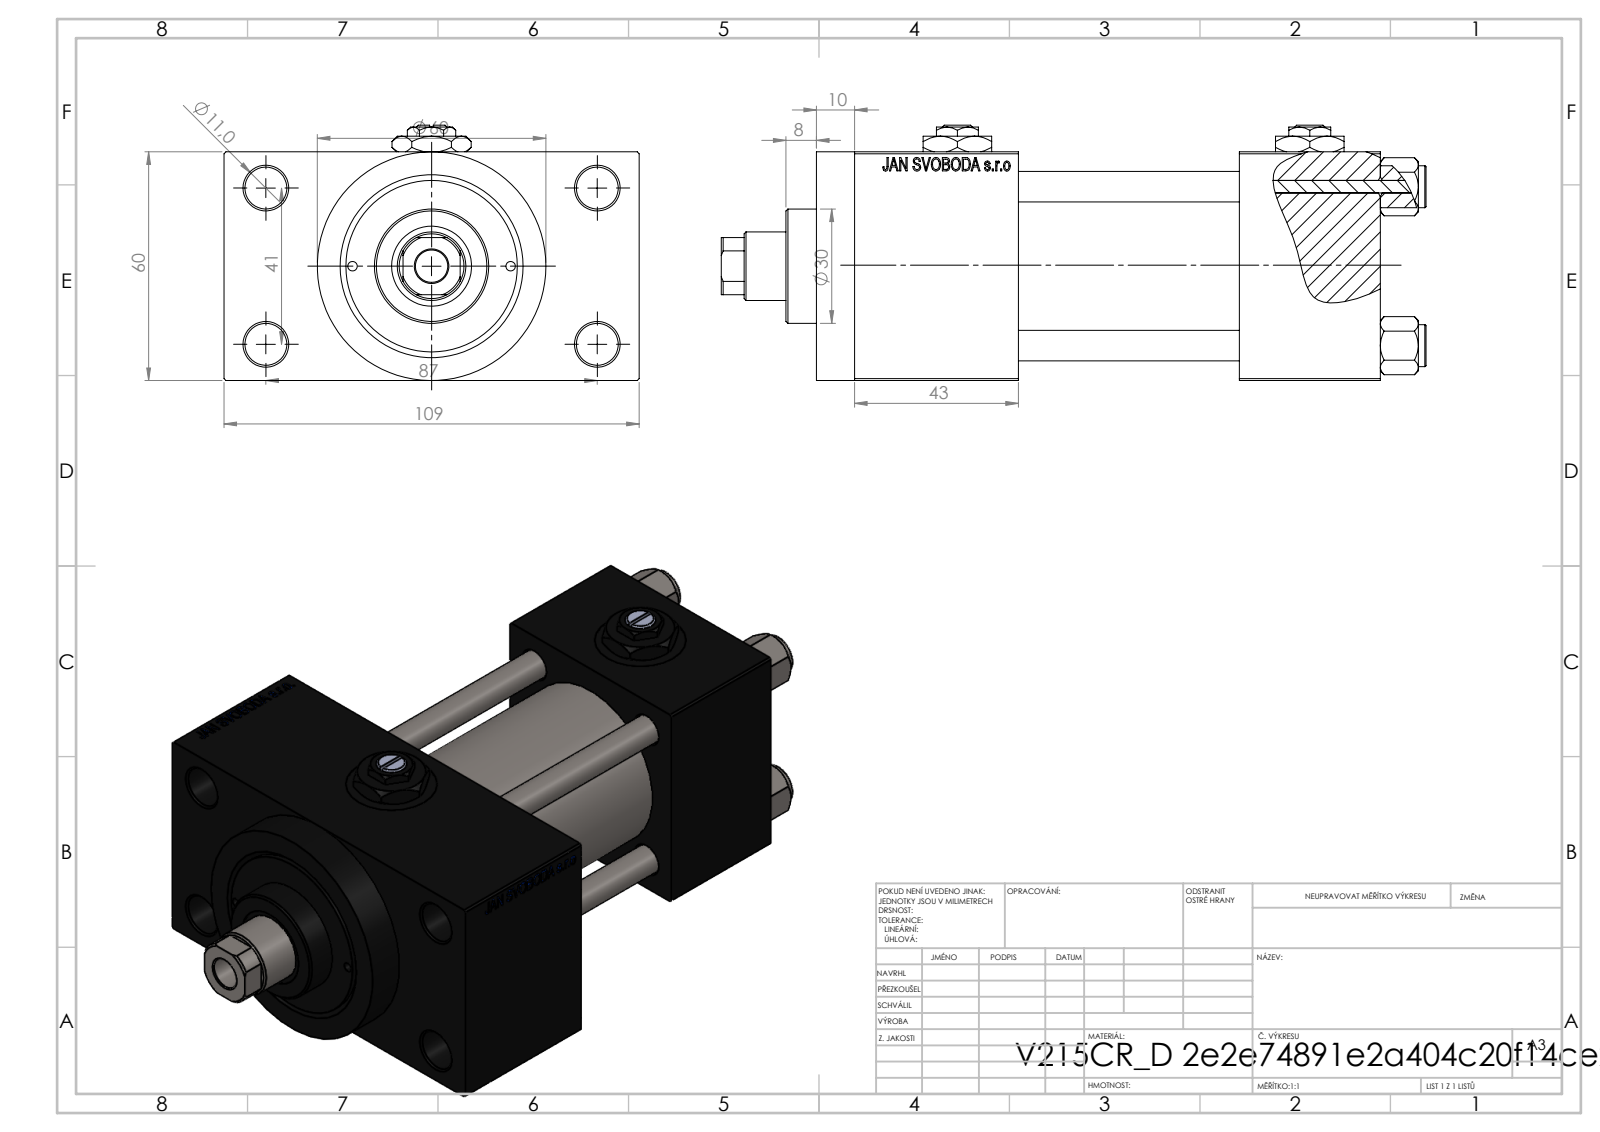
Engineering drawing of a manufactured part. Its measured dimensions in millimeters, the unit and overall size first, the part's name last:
Units: millimetres
Overall size (bounding box): 185 × 109 × 67
Round holes (diameter × count): ⌀8 ×4, ⌀11 ×4, ⌀2.5 ×2, ⌀7 ×2, ⌀16.66 ×2, ⌀24 ×2, ⌀8.5 ×1, ⌀18 ×1, ⌀21 ×1, ⌀31 ×1, ⌀40 ×1, ⌀45 ×1
Round bosses / shafts (diameter × count): ⌀11 ×4, ⌀60 ×1, ⌀46 ×1, ⌀30 ×1
Partial cylindrical surfaces — rounded edges, fillets, slot ends (radius × count): R8.5 ×1
Main face-to-face distances: 60, 24.5, 84.5, 58, 37, 95, 43, 138, 101, 109
Hole centre spacings: 20.85, 22.65, 29.49, 30.62, 41.7, 46.53, 47.15, 48.09
Volume: 515 380 mm³ · Surface area: 123 872 mm²
Bodies: 13 solids, 1214 faces (548 planar, 104 cylindrical, 562 other)
Part name (STEP PRODUCT): Zatka_pro_OIL_PORT; V215CR_VCP_D; V215_VC_A; NUT_M5_D (+2 more)
STEP written by: SolidWorks 2019 (CONFIG_CONTROL_DESIGN)
